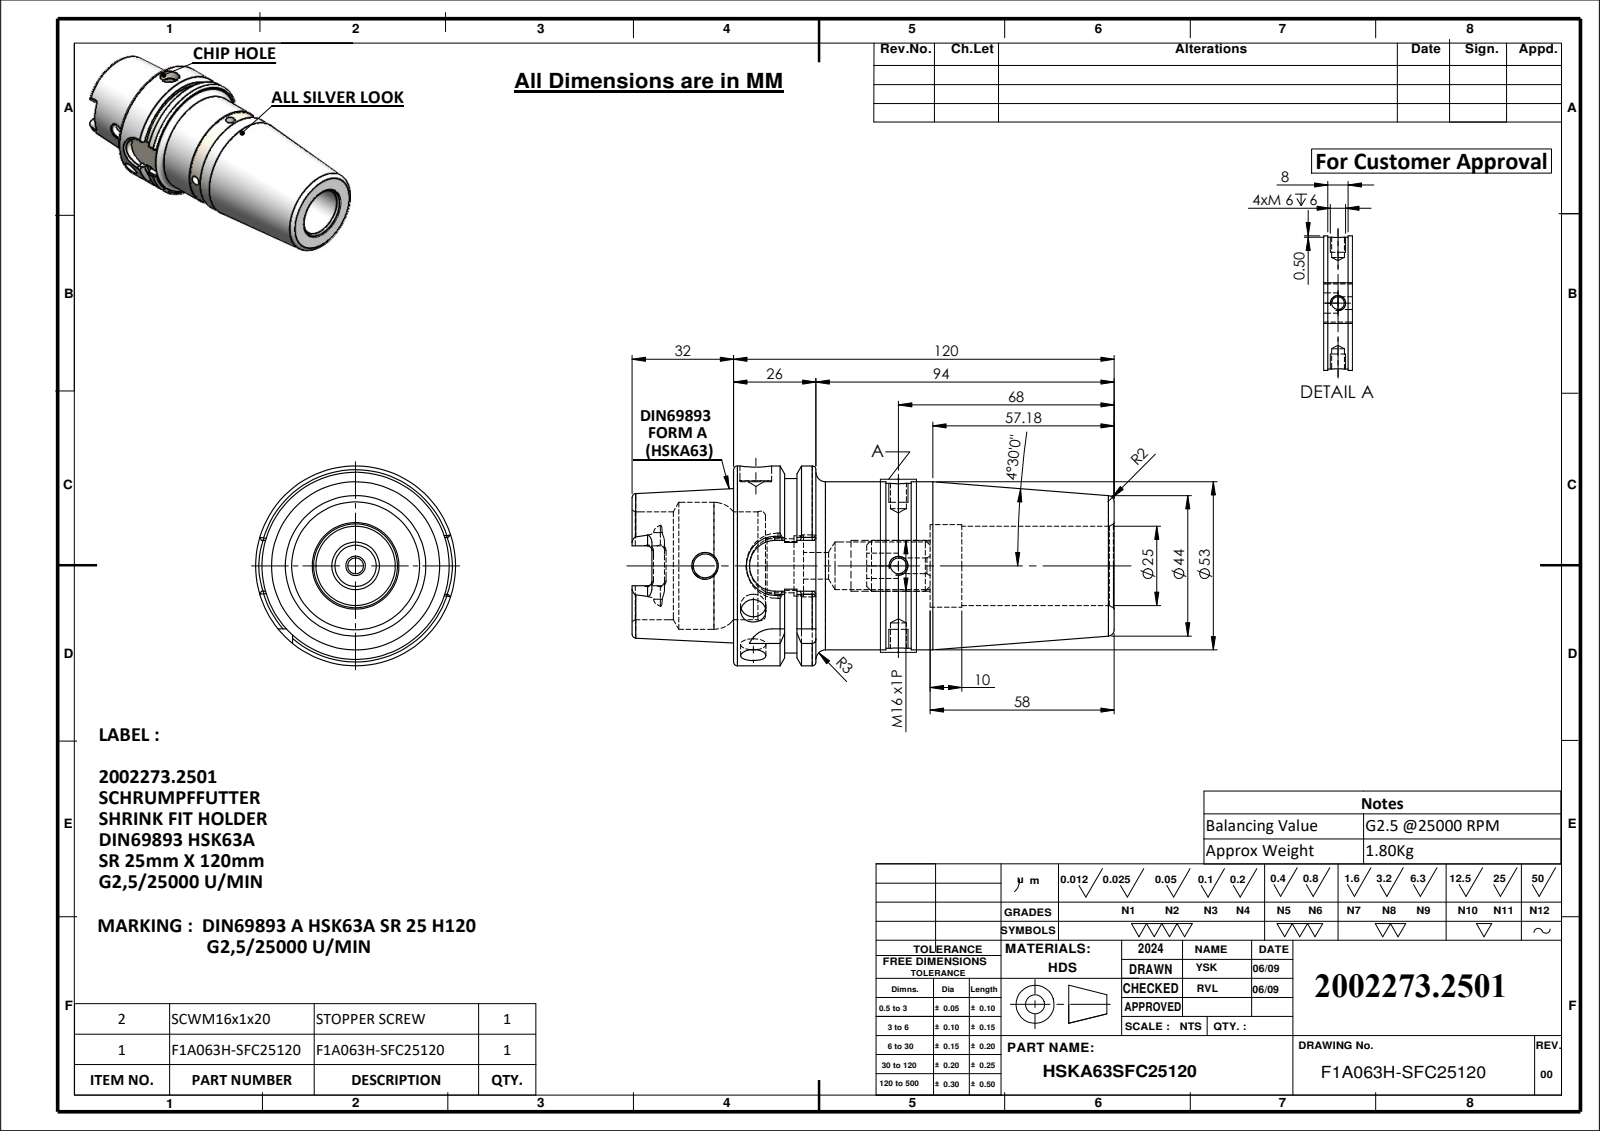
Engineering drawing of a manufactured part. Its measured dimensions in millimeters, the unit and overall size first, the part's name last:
Units: millimetres
Overall size (bounding box): 151.95 × 63 × 63
Round holes (diameter × count): ⌀5 ×3, ⌀8 ×2, ⌀7.5 ×1, ⌀8.4 ×1, ⌀10 ×1, ⌀15 ×1, ⌀17 ×1, ⌀19 ×1, ⌀25 ×1, ⌀26 ×1, ⌀34 ×1, ⌀40 ×1
Round bosses / shafts (diameter × count): ⌀63 ×1, ⌀55 ×1, ⌀53 ×1, ⌀52 ×1, ⌀16 ×1
Partial cylindrical surfaces — rounded edges, fillets, slot ends (radius × count): R1.3 ×6, R2.88 ×4, R8 ×2, R9 ×1
Main face-to-face distances: 119.95, 10, 109.95, 61.95, 51.95, 58, 32, 42, 93.95, 151.95
Hole centre spacings: 44.95, 60.95
Volume: 235 389 mm³ · Surface area: 44 911 mm²
Bodies: 2 solids, 218 faces (67 planar, 69 cylindrical, 82 other)
Part name (STEP PRODUCT): SCWM16X1P; HSKA63SFC25120WW; F1A063H-SFC25120
STEP written by: SolidWorks 2024 (CONFIG_CONTROL_DESIGN)
